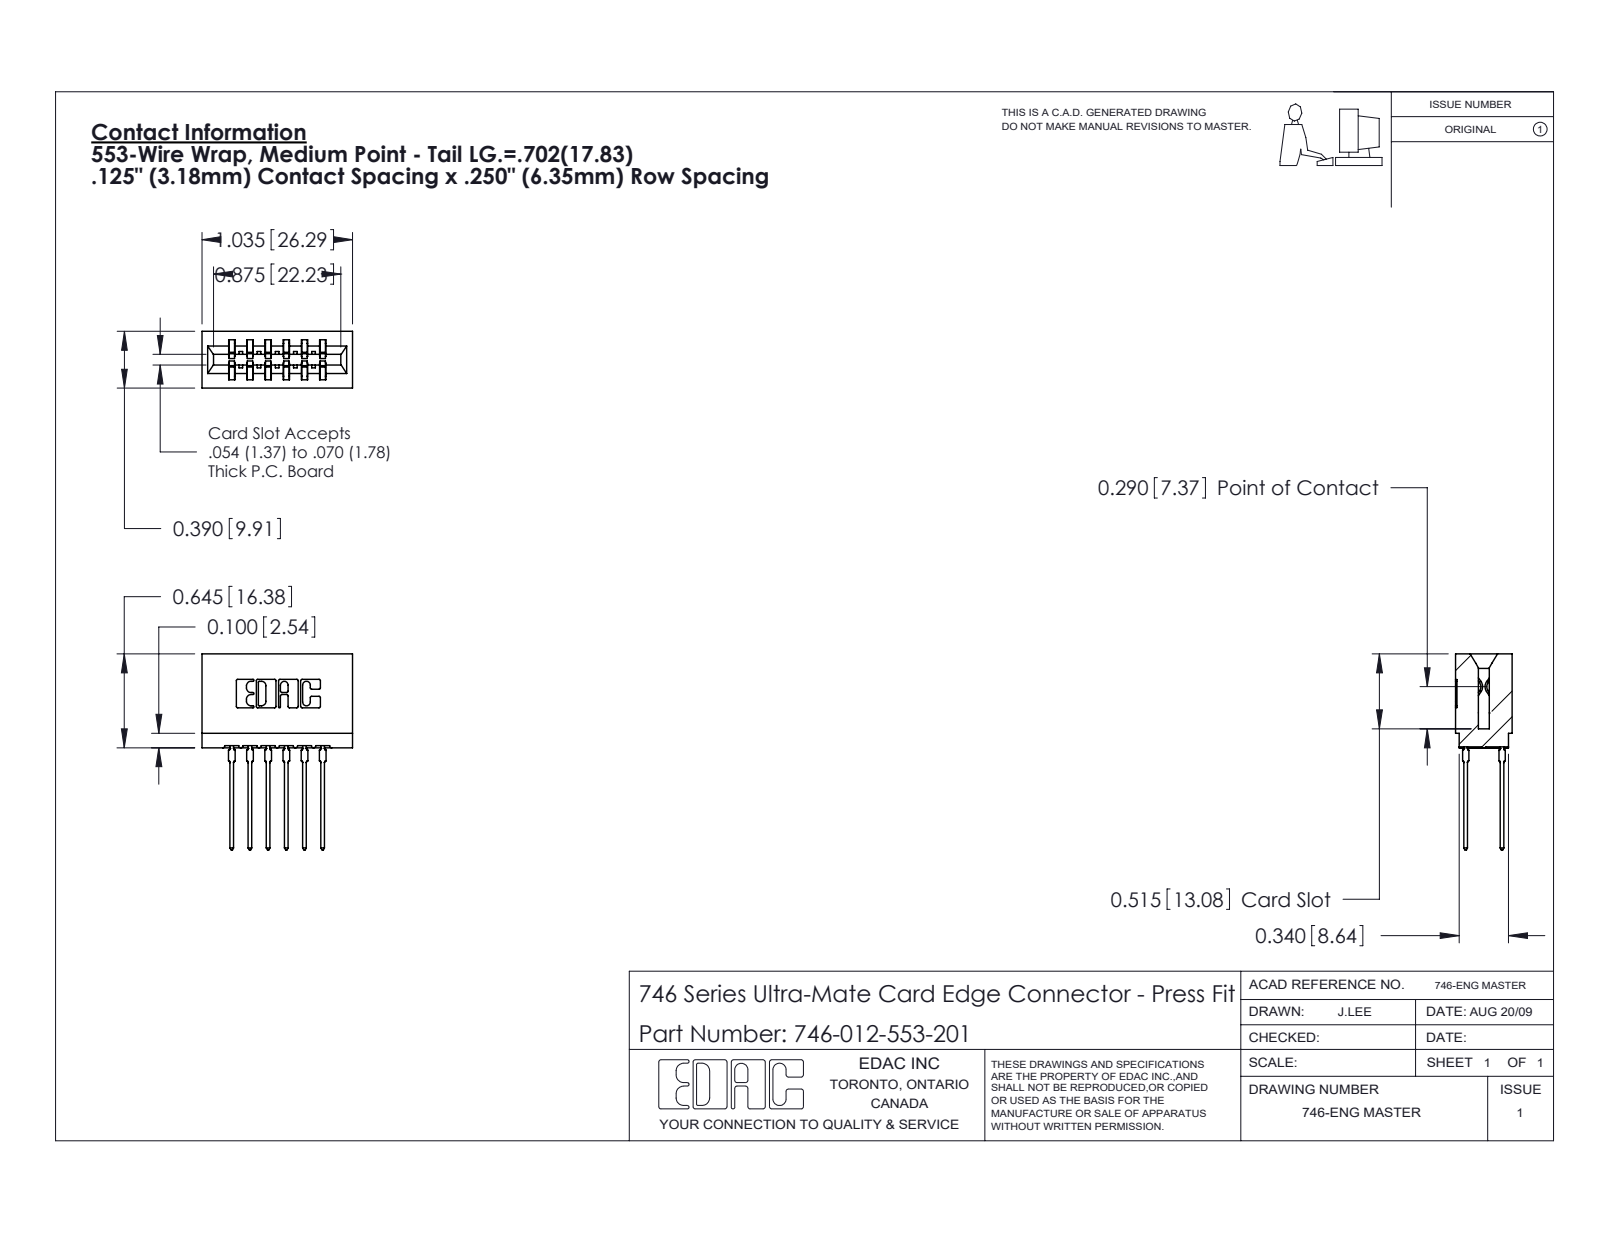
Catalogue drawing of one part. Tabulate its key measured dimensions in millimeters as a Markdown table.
| quantity | value |
| --- | --- |
| part name | 746-292-001_553; 746 Part_.515 Slot Depth - 01; 746-012-553-201 |
| STEP written by | SolidWorks 2020 (CONFIG_CONTROL_DESIGN) |
| units | millimeters |
| bodies | 13 solids, 1171 faces (607 planar, 252 cylindrical, 312 other) |
| overall size | 34.2 × 26.3 × 9.9 |
| volume | 3 100 mm³ |
| surface area | 4 505 mm² |
| partial cylindrical surfaces (radius × count) | 0.5 × 24, 0.3 × 22, 0.1 × 8, 0.3 × 8, 0.4 × 7, 0.2 × 6, 0.8 × 6, 0.7 × 3 |
| main face-to-face distances | 6.4, 1.4, 3.2, 8.5, 1.1, 2.1, 3.2, 0.6, 9.5, 12.7 |
